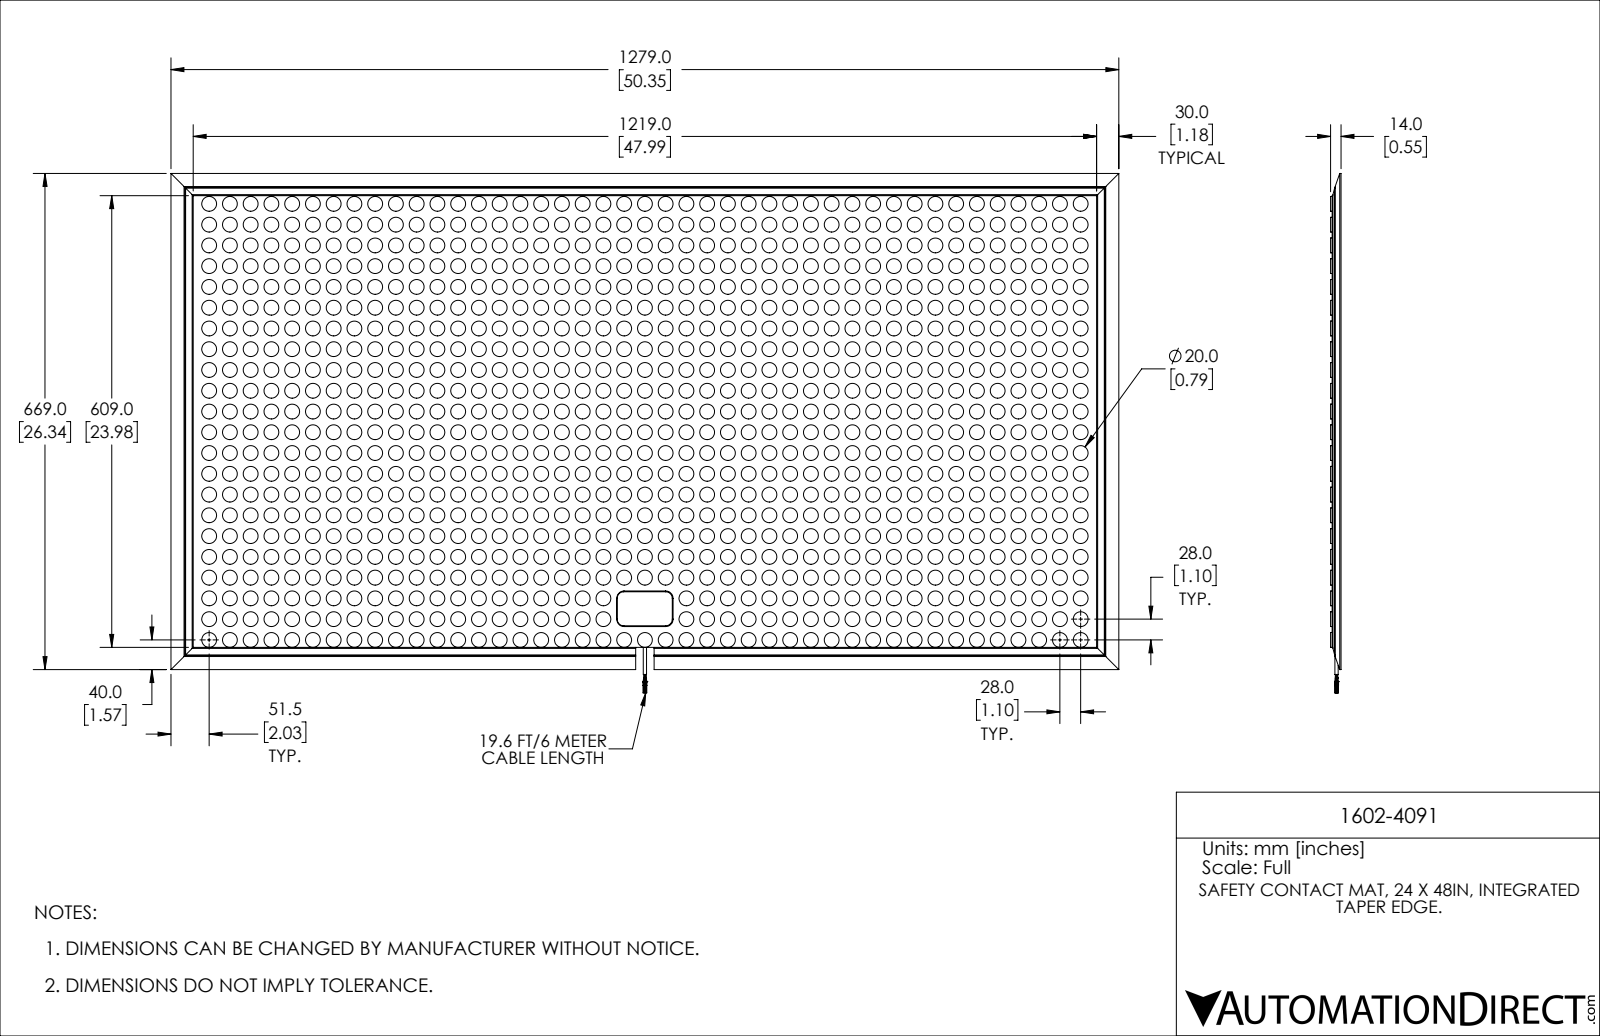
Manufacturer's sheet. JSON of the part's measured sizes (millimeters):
{"part_name": "1602-4091", "step_written_by": "SolidWorks 2021 (AUTOMOTIVE_DESIGN)", "units": "millimeters", "bodies": {"solids": 945, "faces": 3961, "planar": 1958, "cylindrical": 1962, "other": 41}, "overall_size": [1279, 700.5, 14], "volume_mm3": 10120000, "surface_area_mm2": 2535000, "round_bosses_or_shafts": [[20, 940], [1.2, 20], [0.8, 8], [4.4, 1]], "partial_cylinders_radius": [[10, 6], [1, 4]], "face_to_face_distances": [12, 2, 14, 609, 1219, 3.4, 1.4, 10.6, 10.5, 3.5]}
